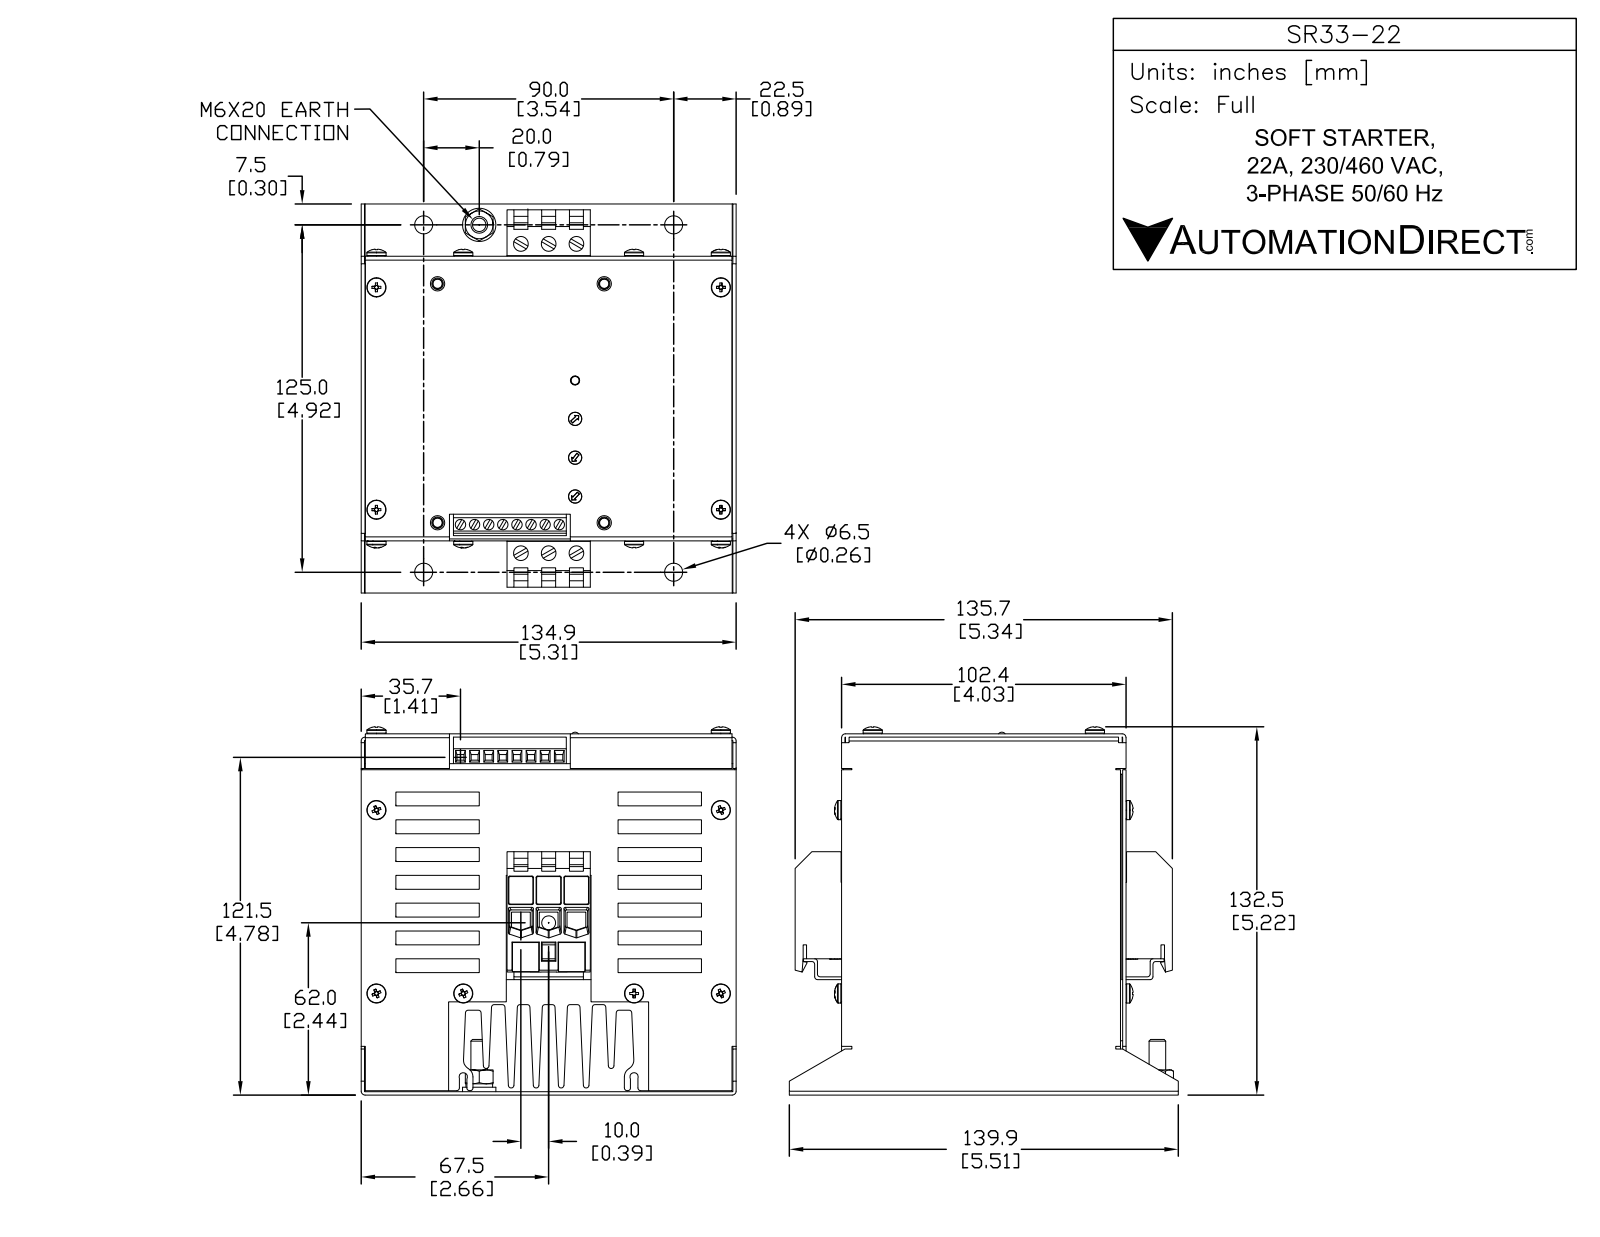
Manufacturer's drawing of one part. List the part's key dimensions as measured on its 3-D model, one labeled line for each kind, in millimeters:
Part name (STEP PRODUCT): SR33-22
STEP written by: SolidWorks 2013 (AUTOMOTIVE_DESIGN)
Units: millimetres
Bodies: 1 solid, 980 faces (712 planar, 170 cylindrical, 98 other)
Overall size (bounding box): 139.9 × 134.9 × 132.9
Volume: 1 475 000 mm³ · Surface area: 260 135 mm²
Round holes (diameter × count): ⌀3.82 ×8, ⌀5 ×6, ⌀6.5 ×4
Round bosses / shafts (diameter × count): ⌀6.9 ×10, ⌀12 ×1, ⌀6 ×1
Partial cylindrical surfaces — rounded edges, fillets, slot ends (radius × count): R1 ×30, R0.44 ×14, R3 ×5, R2 ×4, R0.57 ×3, R0.5 ×2, R0.52 ×2, R0.52 ×2
Main face-to-face distances: 5, 10, 15, 20, 30, 25, 35, 40, 45, 50
Hole centre spacings: 10, 5, 20, 15, 35.55, 45.43, 55.35, 113.02
